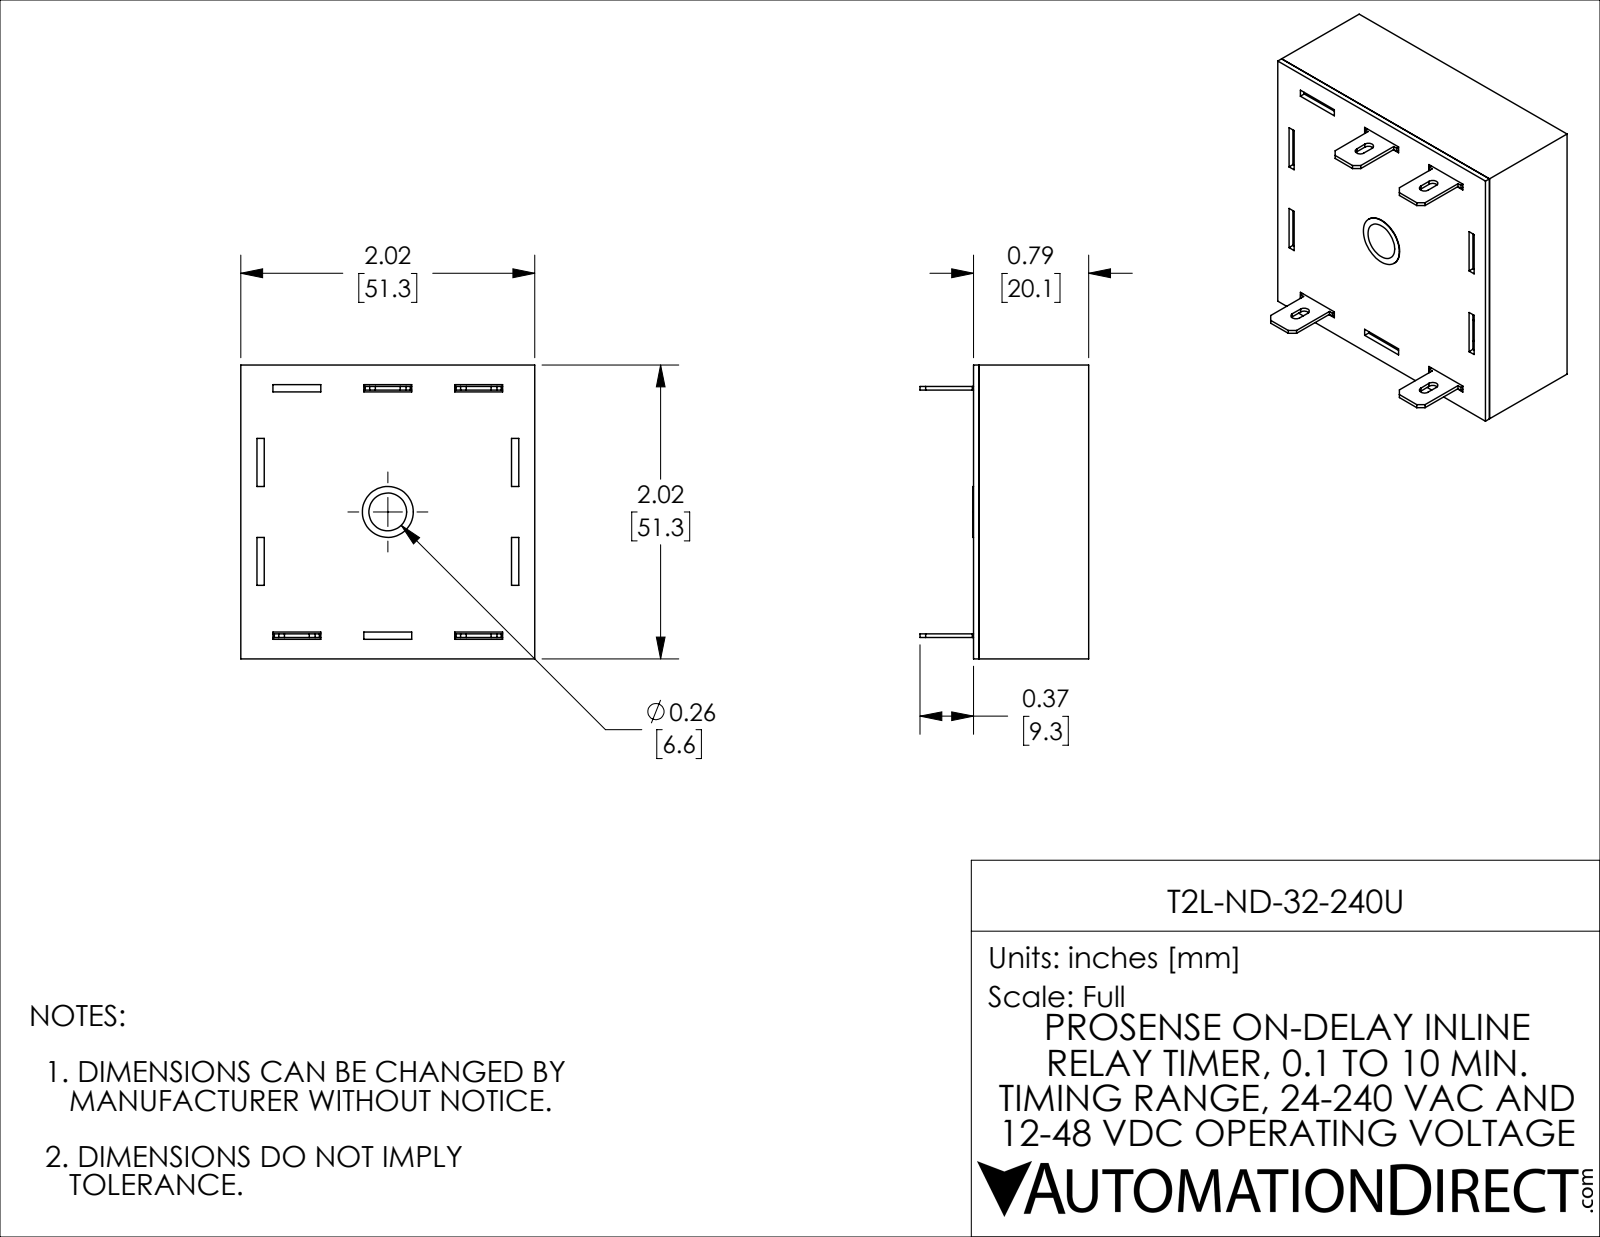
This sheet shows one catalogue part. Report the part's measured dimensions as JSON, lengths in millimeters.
{"part_name": "T2L-ND-32-240U", "step_written_by": "SolidWorks 2021 (CONFIG_CONTROL_DESIGN)", "units": "millimeters", "bodies": {"solids": 6, "faces": 160, "planar": 146, "cylindrical": 12, "other": 2}, "overall_size": [51.31, 51.31, 29.46], "volume_mm3": 10499, "surface_area_mm2": 20889, "round_holes": [[8.89, 1]], "partial_cylinders_radius": [[0.89, 6]], "face_to_face_distances": [1.14, 50.16, 19.15, 20.12, 0.97, 18.01, 18.98, 51.3, 49.02, 43.18]}
